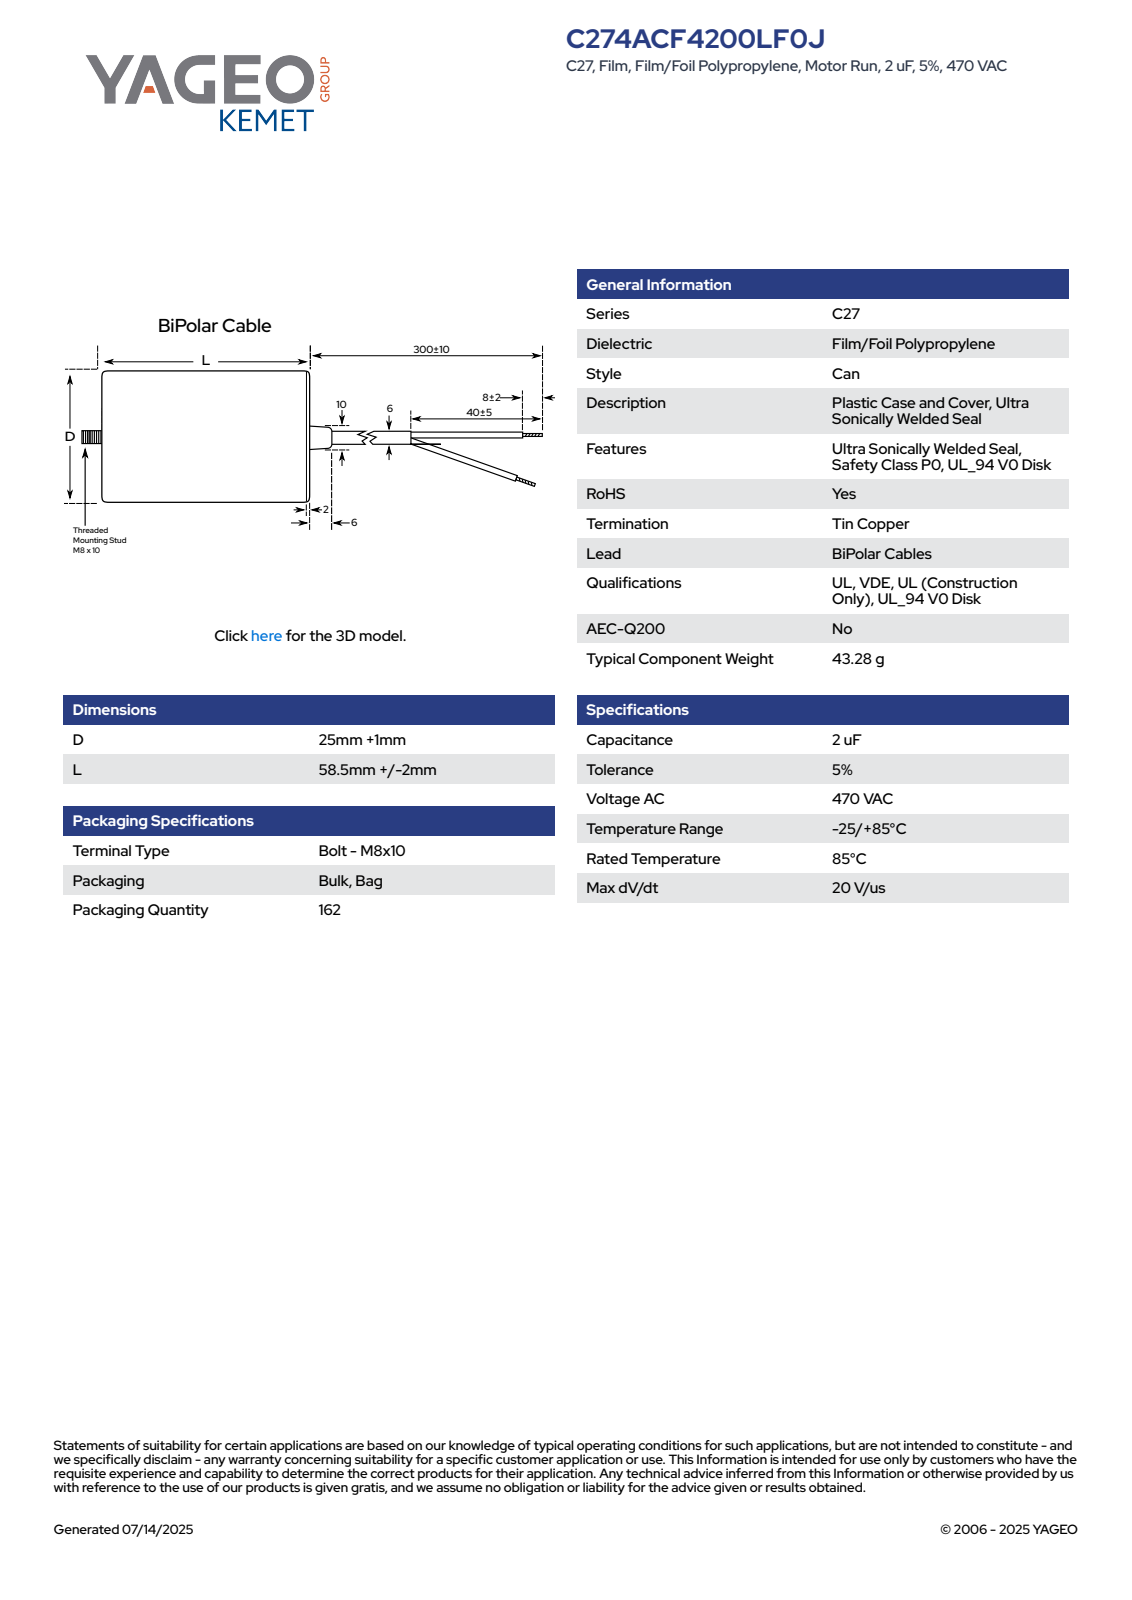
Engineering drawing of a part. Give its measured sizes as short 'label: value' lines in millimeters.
name: CFM_KC27BI_25X58.5_D26L60.5
written by: SolidWorks 2014 (AUTOMOTIVE_DESIGN)
unit: mm
bodies: 2 solids, 82 faces (28 planar, 15 cylindrical, 39 other)
size: 76.5 × 26.01 × 26
volume: 32 210 mm³; area: 6 617 mm²
holes: 1× ⌀22
bosses: 1× ⌀26, 1× ⌀8
rounds: 1× R13.01
face distances: 58.5, 60.5, 2, 10, 68.5, 70.5, 76.5, 66.5, 8, 6
